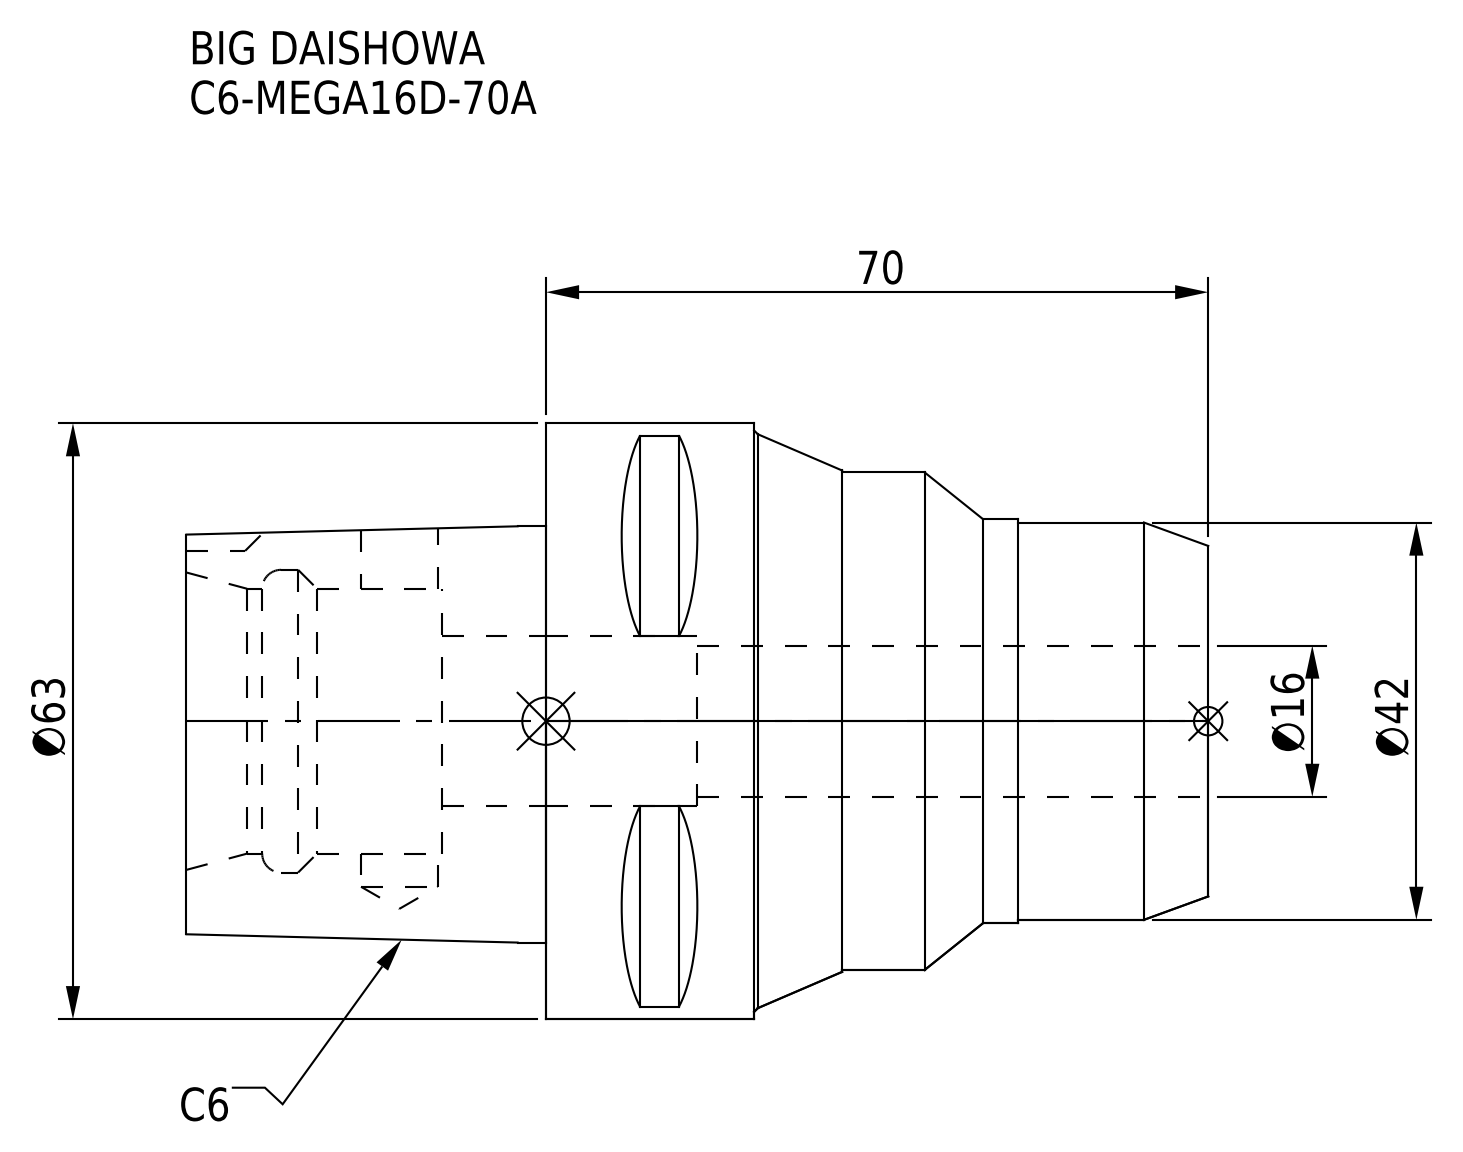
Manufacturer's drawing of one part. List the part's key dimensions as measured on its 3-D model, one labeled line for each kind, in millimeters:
Part name (STEP PRODUCT): C6-MEGA16D-70A
STEP written by: CREO PARAMETRIC BY PTC INC, 2016380 (AUTOMOTIVE_DESIGN)
Units: millimetres
Bodies: 1 solid, 71 faces (30 planar, 23 cylindrical, 18 other)
Overall size (bounding box): 108 × 63 × 63
Volume: 171 595 mm³ · Surface area: 28 267 mm²
Round holes (diameter × count): ⌀8.1 ×1, ⌀16 ×1, ⌀18 ×1, ⌀28 ×1, ⌀32 ×1
Round bosses / shafts (diameter × count): ⌀63 ×1, ⌀52.6 ×1, ⌀42.7 ×1, ⌀42 ×1
Partial cylindrical surfaces — rounded edges, fillets, slot ends (radius × count): R5 ×1
Main face-to-face distances: 70, 108, 38, 27, 81, 11, 24.89, 55.4, 48, 22
